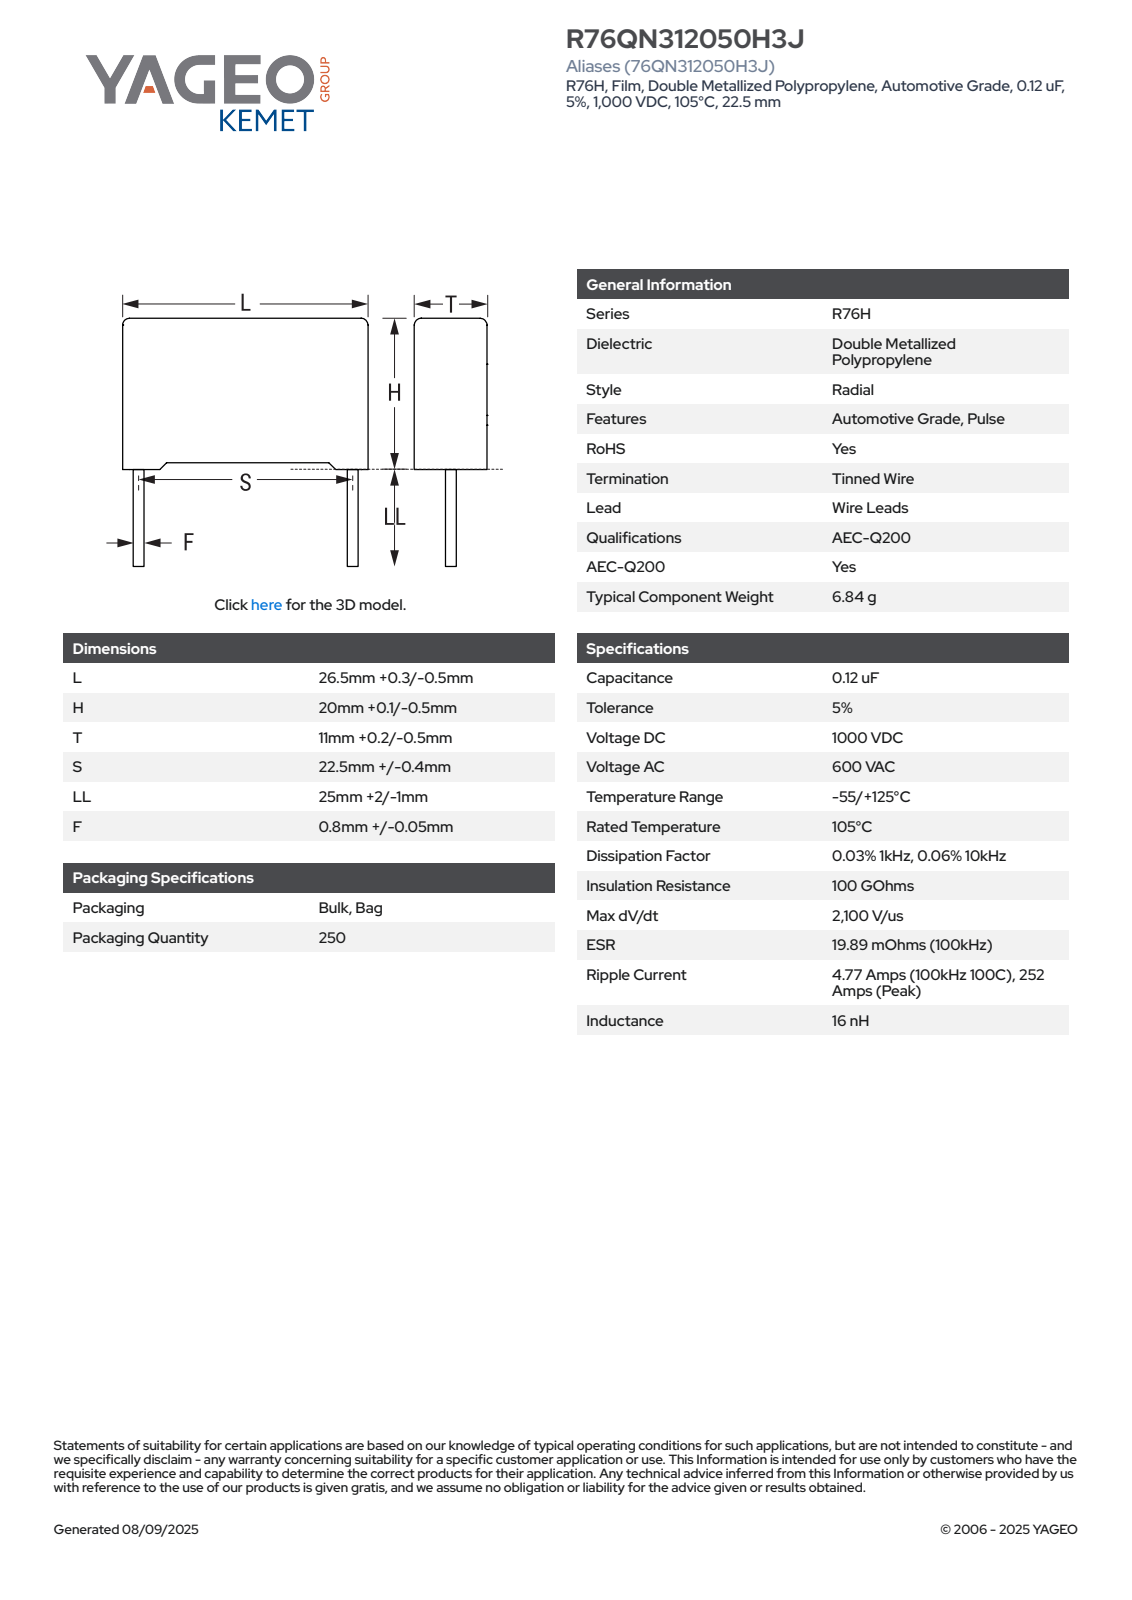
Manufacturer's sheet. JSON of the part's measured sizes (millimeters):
{"part_name": "CFR_RB2R76_26.5X20X11_L26.8H20.1T11.2S22.5LL27F0.85", "step_written_by": "SolidWorks 2014 (AUTOMOTIVE_DESIGN)", "units": "millimeters", "bodies": {"solids": 4, "faces": 85, "planar": 77, "cylindrical": 8, "other": 0}, "overall_size": [47.1, 26.8, 11.21], "volume_mm3": 5861, "surface_area_mm2": 2314, "round_bosses_or_shafts": [[0.85, 2]], "partial_cylinders_radius": [[0.5, 4]], "face_to_face_distances": [11.2, 19.35, 26.8, 19.41, 0.75, 0.69, 20.1, 0.89, 25.91, 11.21]}
